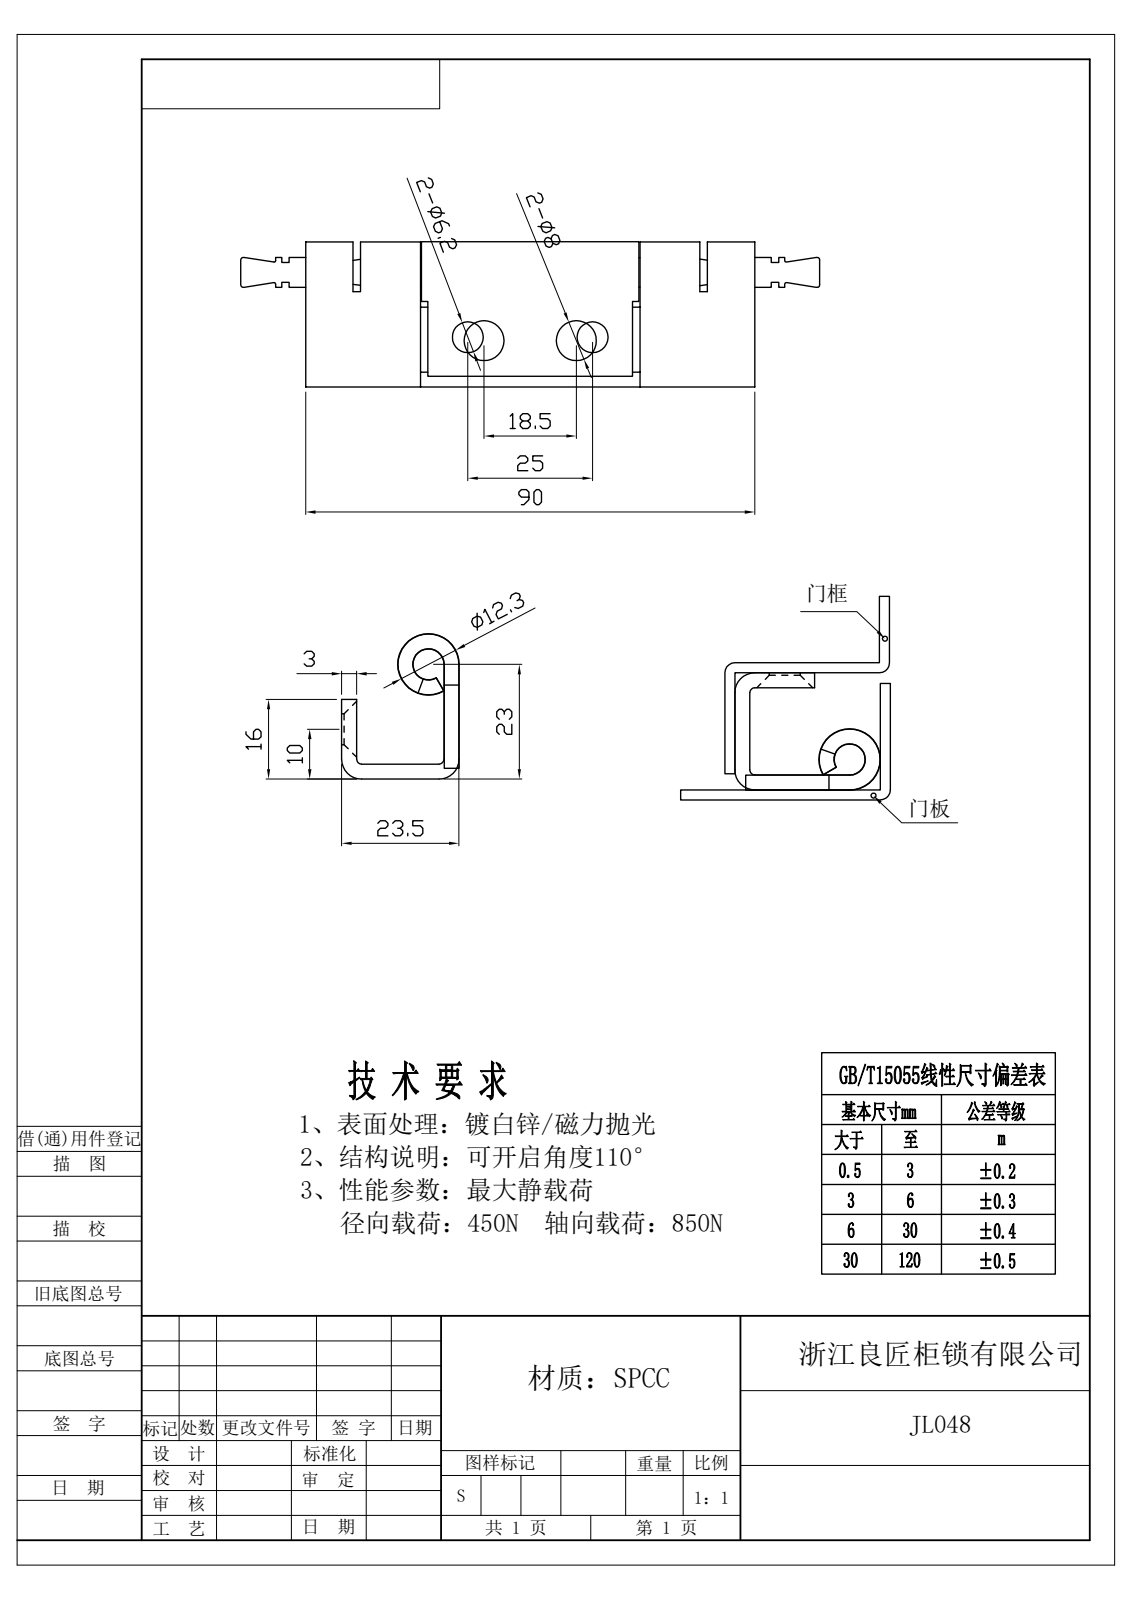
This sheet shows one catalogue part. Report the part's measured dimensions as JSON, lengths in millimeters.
{"step_written_by": "Rhino 8.5 (CONFIG_CONTROL_DESIGN)", "units": "millimeters", "bodies": {"solids": 3, "faces": 139, "planar": 65, "cylindrical": 48, "other": 26}, "overall_size": [116, 43.89, 23.55], "volume_mm3": 7912, "surface_area_mm2": 17534, "round_holes": [[6.2, 3], [8, 2], [6.3, 1]], "round_bosses_or_shafts": [[12.3, 1], [12.2, 1], [6, 1], [4.3, 1]], "partial_cylinders_radius": [[0.5, 4], [2, 4], [1, 2], [4, 2]], "face_to_face_distances": [3, 20.5, 17.5, 23.5, 13, 23, 67, 16, 90, 23.2], "hole_center_spacings": [18.5, 25]}
